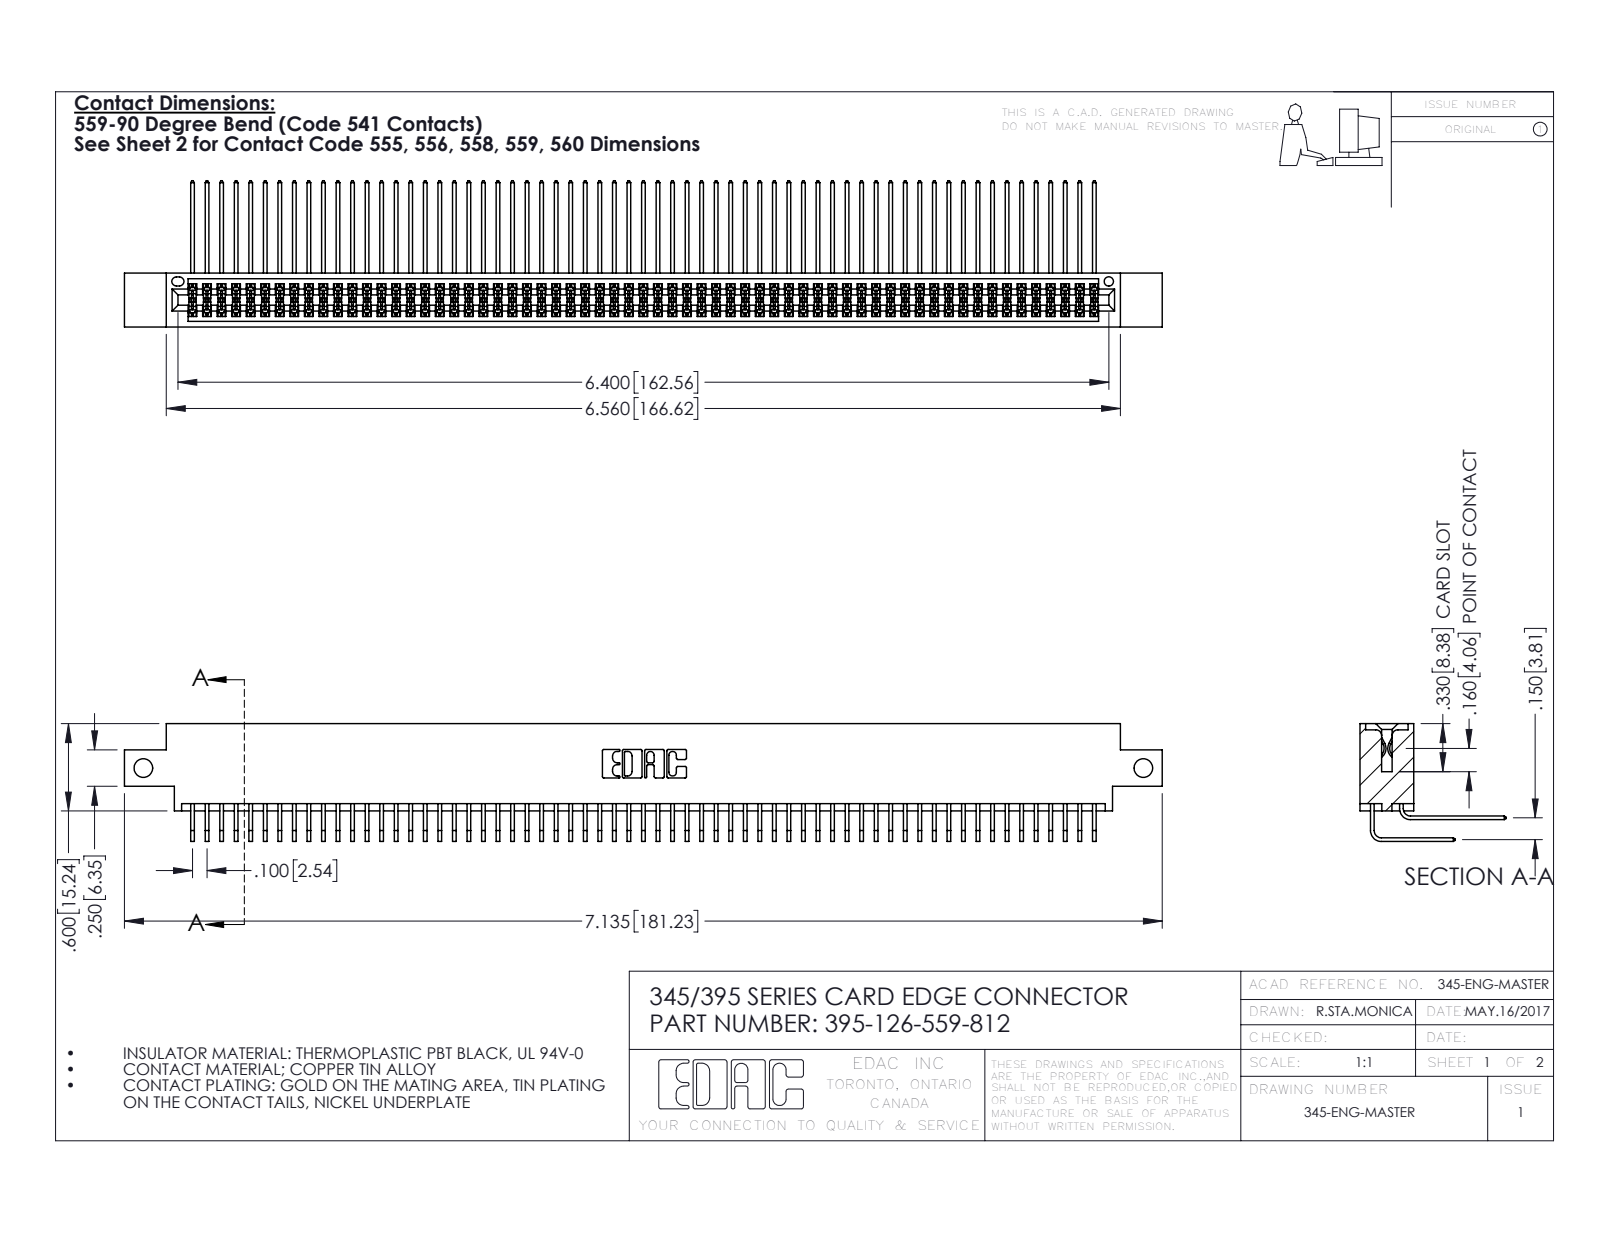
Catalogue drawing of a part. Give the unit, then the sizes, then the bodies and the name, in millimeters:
Units: millimetres
Overall size (bounding box): 181.2 × 25.5 × 20.5
Round holes (diameter × count): ⌀3.3 ×2, ⌀1.6 ×1
Partial cylindrical surfaces — rounded edges, fillets, slot ends (radius × count): R0.2 ×189, R0.3 ×22, R0.2 ×6, R0.8 ×6, R0.7 ×3, R0.4 ×2, R0.5 ×2, R0.6 ×2
Main face-to-face distances: 1.8, 7.6, 9.4, 5.1, 2.5, 6.9, 0.6, 5.7, 4.4, 3.8
Hole centre spacings: 174.6
Volume: 18 320 mm³ · Surface area: 30 920 mm²
Bodies: 127 solids, 6682 faces (4494 planar, 2188 cylindrical, 0 other)
Part name (STEP PRODUCT): 395-126-559-812; 345 Part_0.170 Offset - Side Mount; 345-292-001_559 Tail - 2; 345-292-001_558 559 Tail - 1
STEP written by: SolidWorks 2016 (CONFIG_CONTROL_DESIGN)
